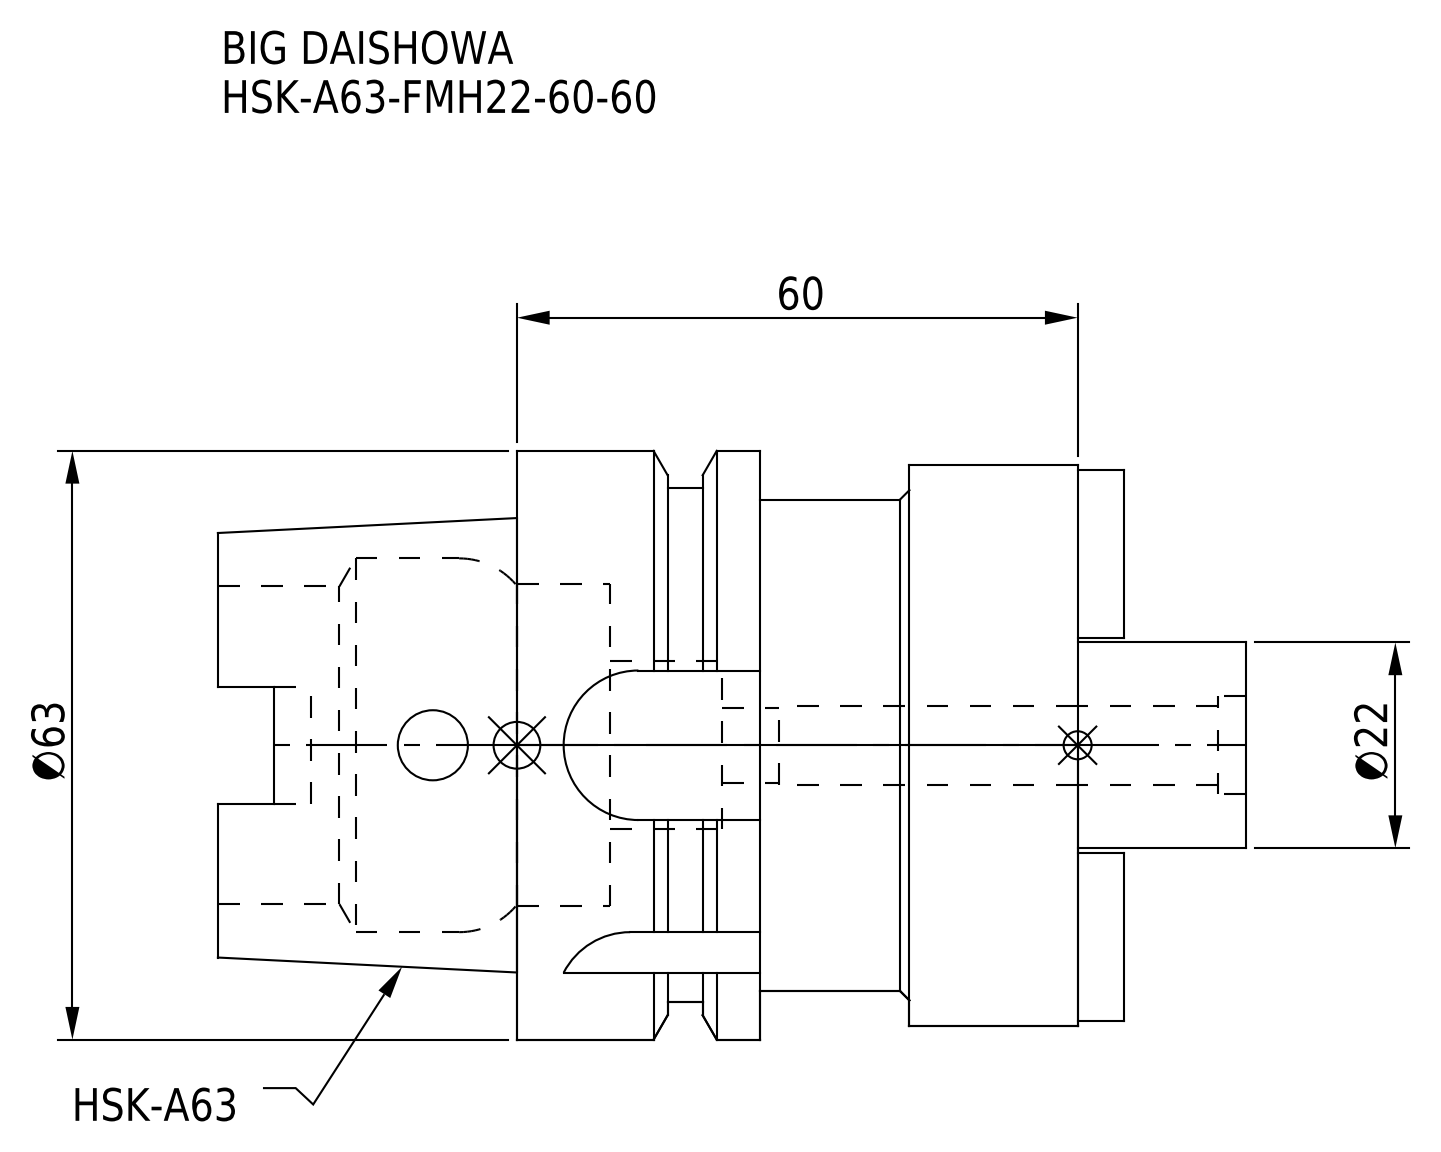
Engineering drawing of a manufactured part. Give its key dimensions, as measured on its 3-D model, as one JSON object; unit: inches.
{"part_name": "HSK-A63-FMH22-60-60", "step_written_by": "CREO PARAMETRIC BY PTC INC, 2016380 (AUTOMOTIVE_DESIGN)", "units": "inches", "bodies": {"solids": 1, "faces": 97, "planar": 45, "cylindrical": 38, "other": 14}, "overall_size": [4.331, 2.48, 2.48], "volume_in3": 10.57, "surface_area_in2": 51, "round_holes": [[0.295, 1], [0.315, 1], [0.335, 1], [0.413, 1], [0.709, 1], [1.339, 1], [1.358, 1], [1.575, 1]], "round_bosses_or_shafts": [[2.48, 1], [2.362, 1], [2.165, 1], [2.071, 1], [0.866, 1]], "partial_cylinders_radius": [[0.315, 2], [0.354, 1]], "face_to_face_distances": [2.362, 0.709, 1.024, 1.339, 1.97, 0.632, 0.392, 1.26, 3.622, 2.283]}
